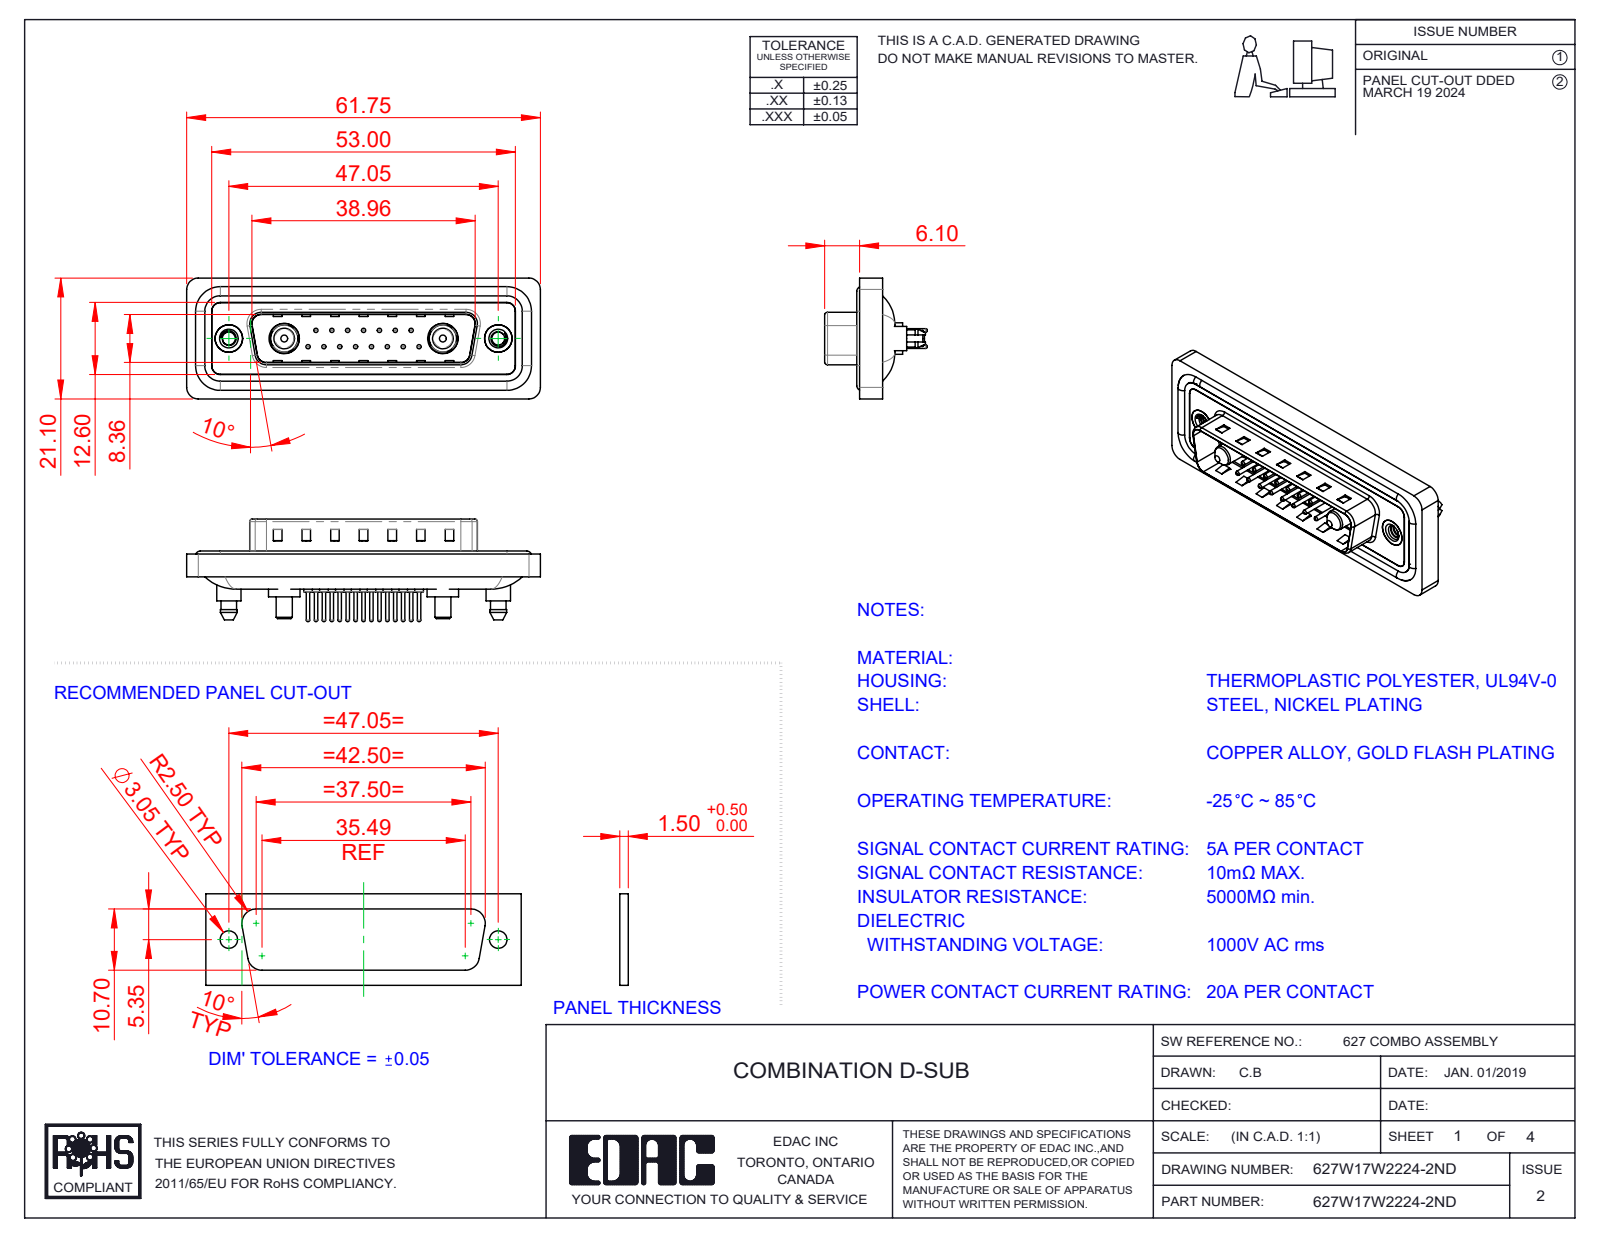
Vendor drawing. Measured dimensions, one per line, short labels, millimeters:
name: 627Combo Housing_17W2; 627Combo Threaded Boardlock_5; 627W17W2224-2ND; 627Combo Contact Row 2_24 (+6 more)
written by: SolidWorks 2023 (CONFIG_CONTROL_DESIGN)
unit: mm
bodies: 26 solids, 1174 faces (350 planar, 476 cylindrical, 348 other)
size: 61.75 × 21.1 × 17.9
volume: 7 401 mm³; area: 12 250 mm²
holes: 15× ⌀0.75, 15× ⌀1.6, 15× ⌀2, 2× ⌀2.26, 2× ⌀4, 2× ⌀4.8, 2× ⌀4.85, 2× ⌀5, 2× ⌀5.3
bosses: 15× ⌀1.5, 15× ⌀0.6, 4× ⌀1.6, 2× ⌀5.5, 2× ⌀5.4, 2× ⌀5.2, 2× ⌀4.9, 2× ⌀4.75
rounds: 24× R1.5, 18× R2, 10× R1.6, 8× R0.5, 4× R0.25, 4× R0.6, 4× R0.65, 4× R0.9
face distances: 0.4, 1.5, 1.1, 1.6, 0.5, 3.1, 2.9, 0.82, 9.58, 4.1
hole spacings: 3.16, 2.77, 5.54, 8.31, 5.04, 7.49, 11.08, 5.03
